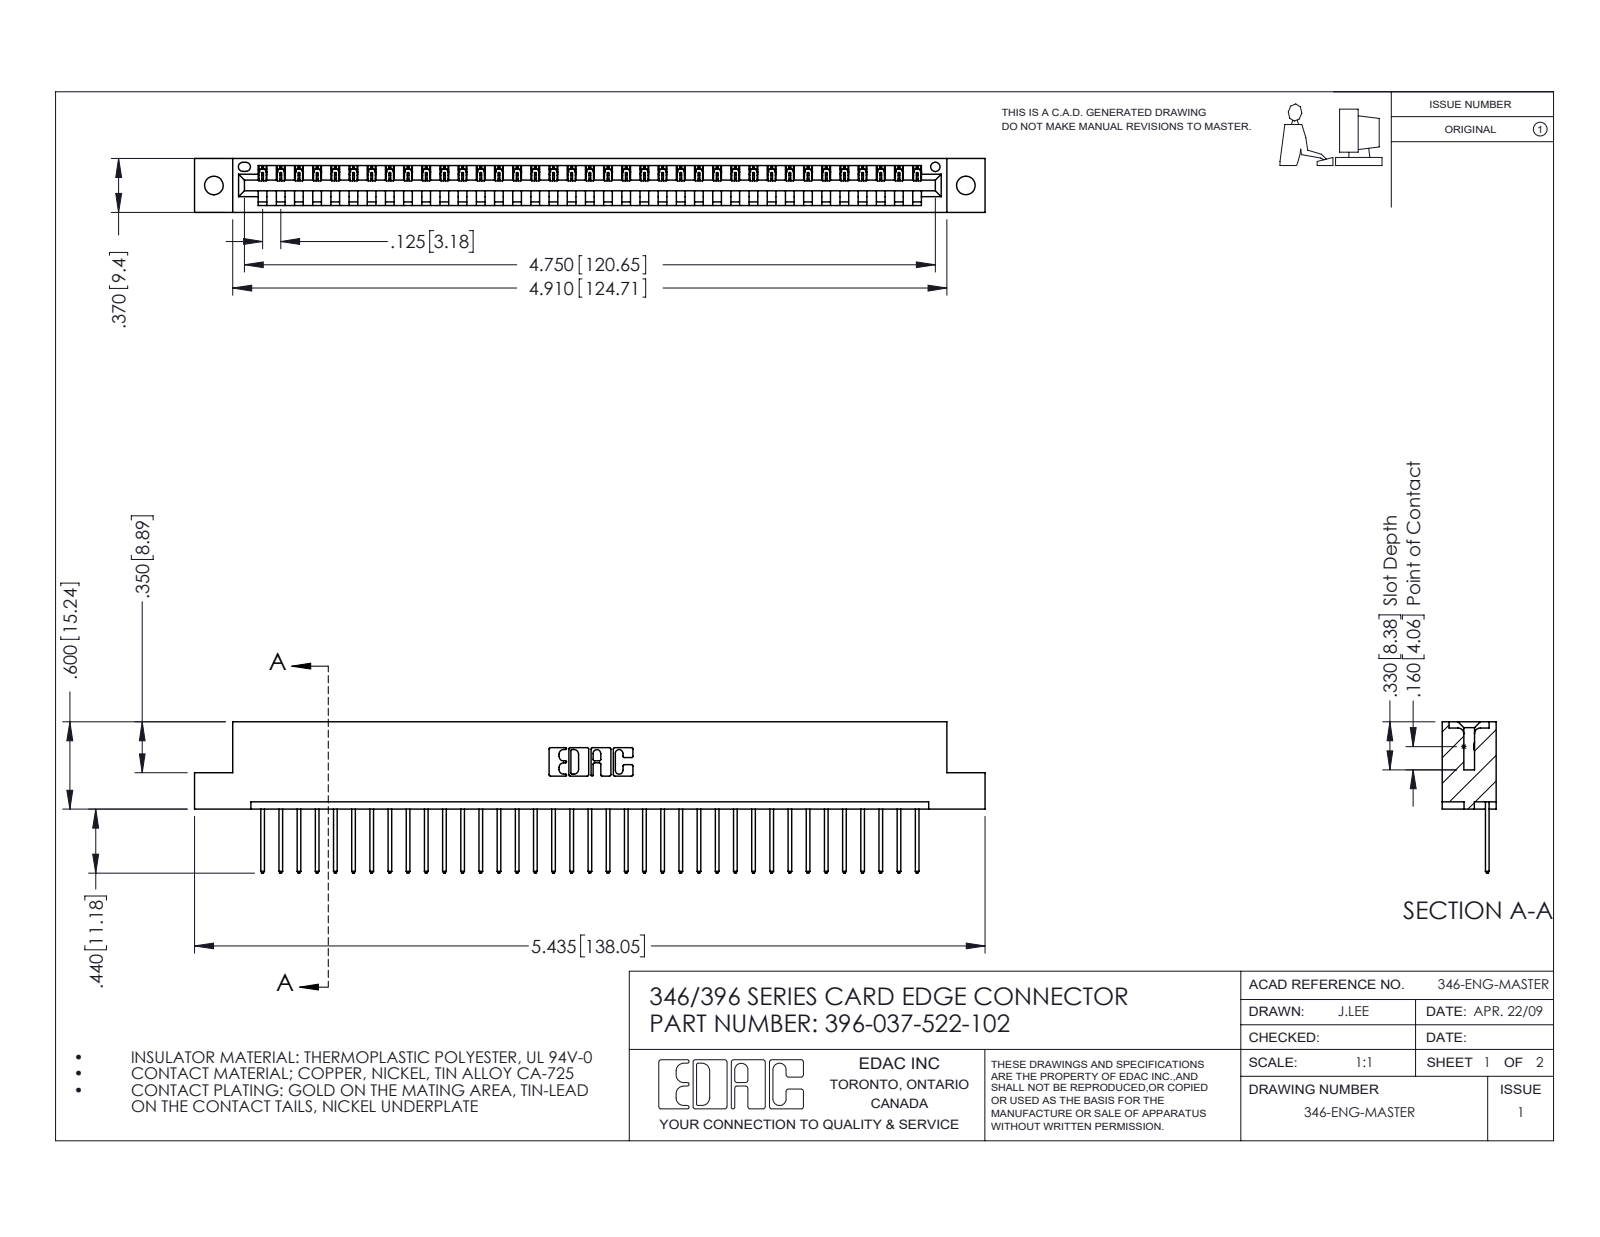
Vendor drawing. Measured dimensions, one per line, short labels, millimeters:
name: 396-037-522-102; 346 Part_Flush Mounting Lugs - 0.128 Dia; 345-292-001_345-293-122
written by: SolidWorks 2016 (CONFIG_CONTROL_DESIGN)
unit: mm
bodies: 38 solids, 2268 faces (1556 planar, 712 cylindrical, 0 other)
size: 138 × 26.4 × 9.4
volume: 13 100 mm³; area: 16 250 mm²
holes: 2× ⌀3.3, 1× ⌀1.6
rounds: 74× R0.2, 74× R0.3, 22× R0.3, 6× R0.2, 6× R0.8, 3× R0.7, 2× R0.8, 2× R1
face distances: 1.2, 8.2, 9.4, 6.4, 1.8, 7.6, 0.6, 3.8, 5.6, 2.5
hole spacings: 6.2, 126, 131.3
